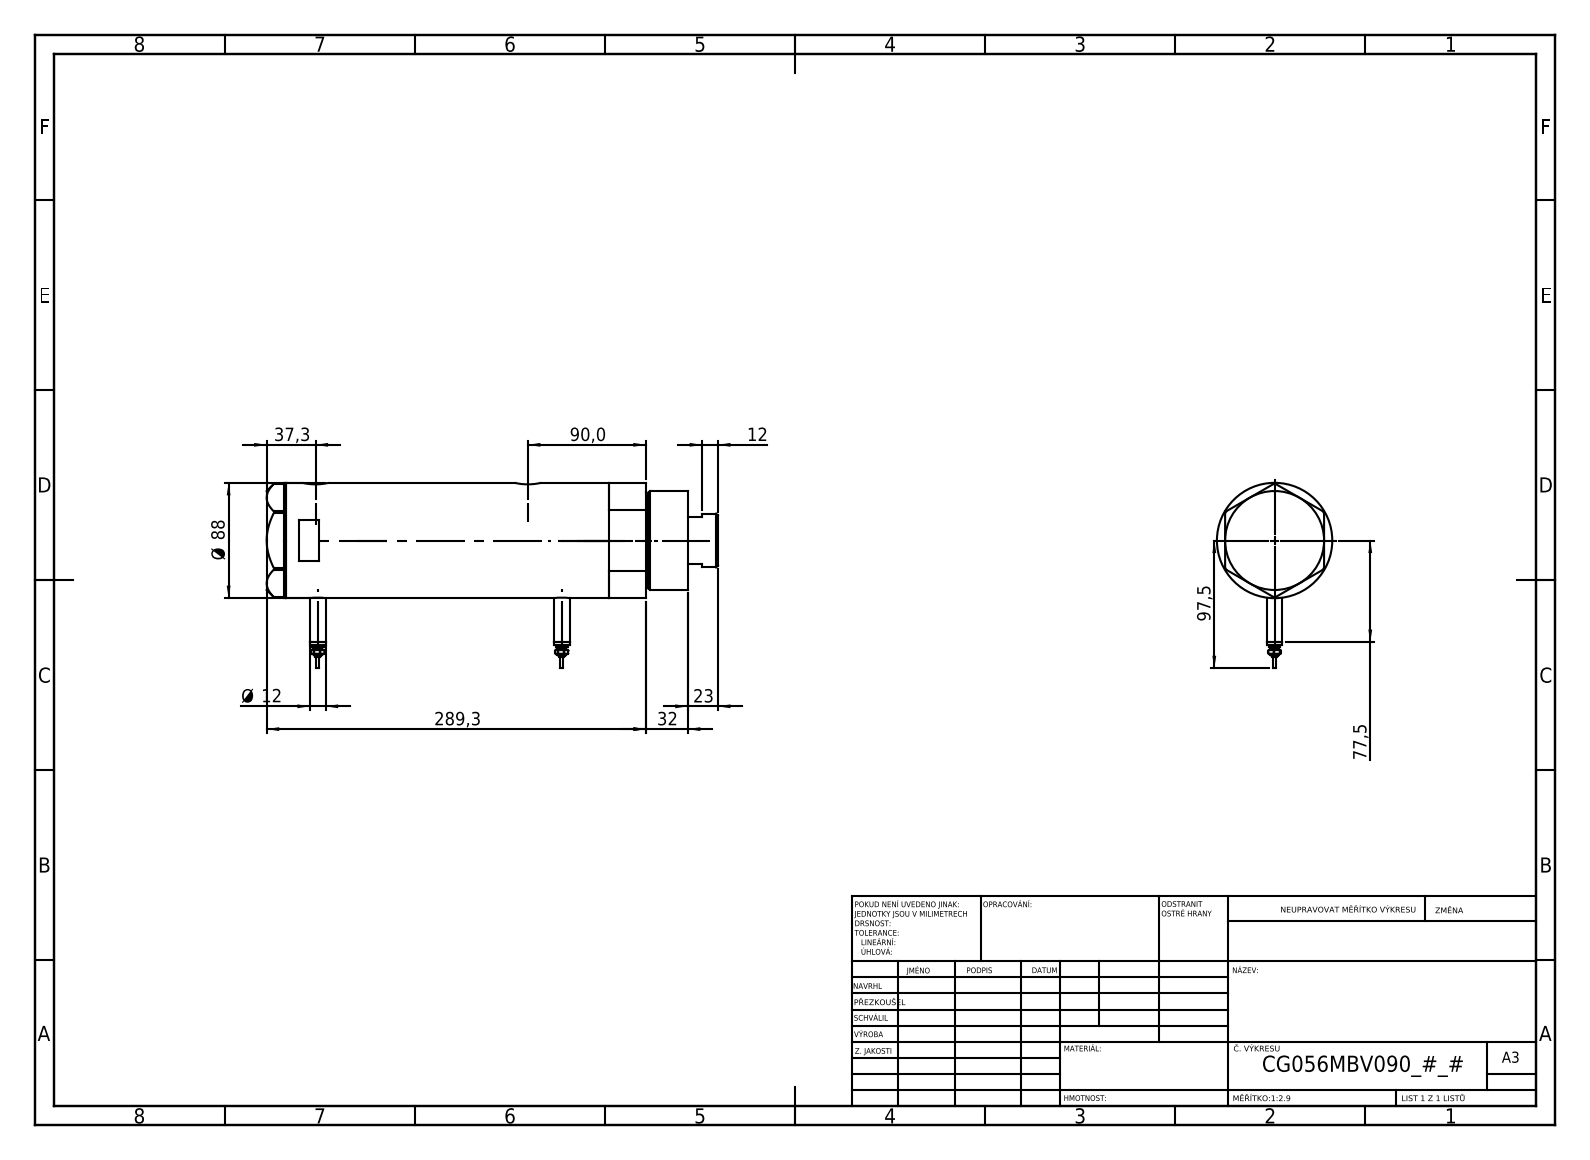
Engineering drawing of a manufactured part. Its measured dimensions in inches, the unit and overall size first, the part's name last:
Units: inches
Overall size (bounding box): 13.555 × 5.571 × 3.465
Round holes (diameter × count): ⌀0.492 ×2, ⌀0.518 ×2, ⌀0.787 ×2, ⌀0.571 ×1, ⌀1.654 ×1, ⌀1.713 ×1, ⌀2.205 ×1, ⌀2.362 ×1, ⌀3.15 ×1
Round bosses / shafts (diameter × count): ⌀0.472 ×2, ⌀0.354 ×2, ⌀0.276 ×2, ⌀0.177 ×2, ⌀0.098 ×2, ⌀3.465 ×1, ⌀2.953 ×1, ⌀2.874 ×1
Main face-to-face distances: 7.26, 1.024, 6.236, 0.591, 1.614, 7.85, 12.059, 12.65, 11.035, 4.799
Hole centre spacings: 0.067, 1.016, 6.311, 6.378, 7.327, 7.394
Volume: 110 in³ · Surface area: 394.1 in²
Bodies: 6 solids, 213 faces (80 planar, 69 cylindrical, 64 other)
Part name (STEP PRODUCT): V270CG_MIDDLE; V270CG_FRONT; Switch; V270CG_BACK (+1 more)
STEP written by: SolidWorks 2019 (CONFIG_CONTROL_DESIGN)
